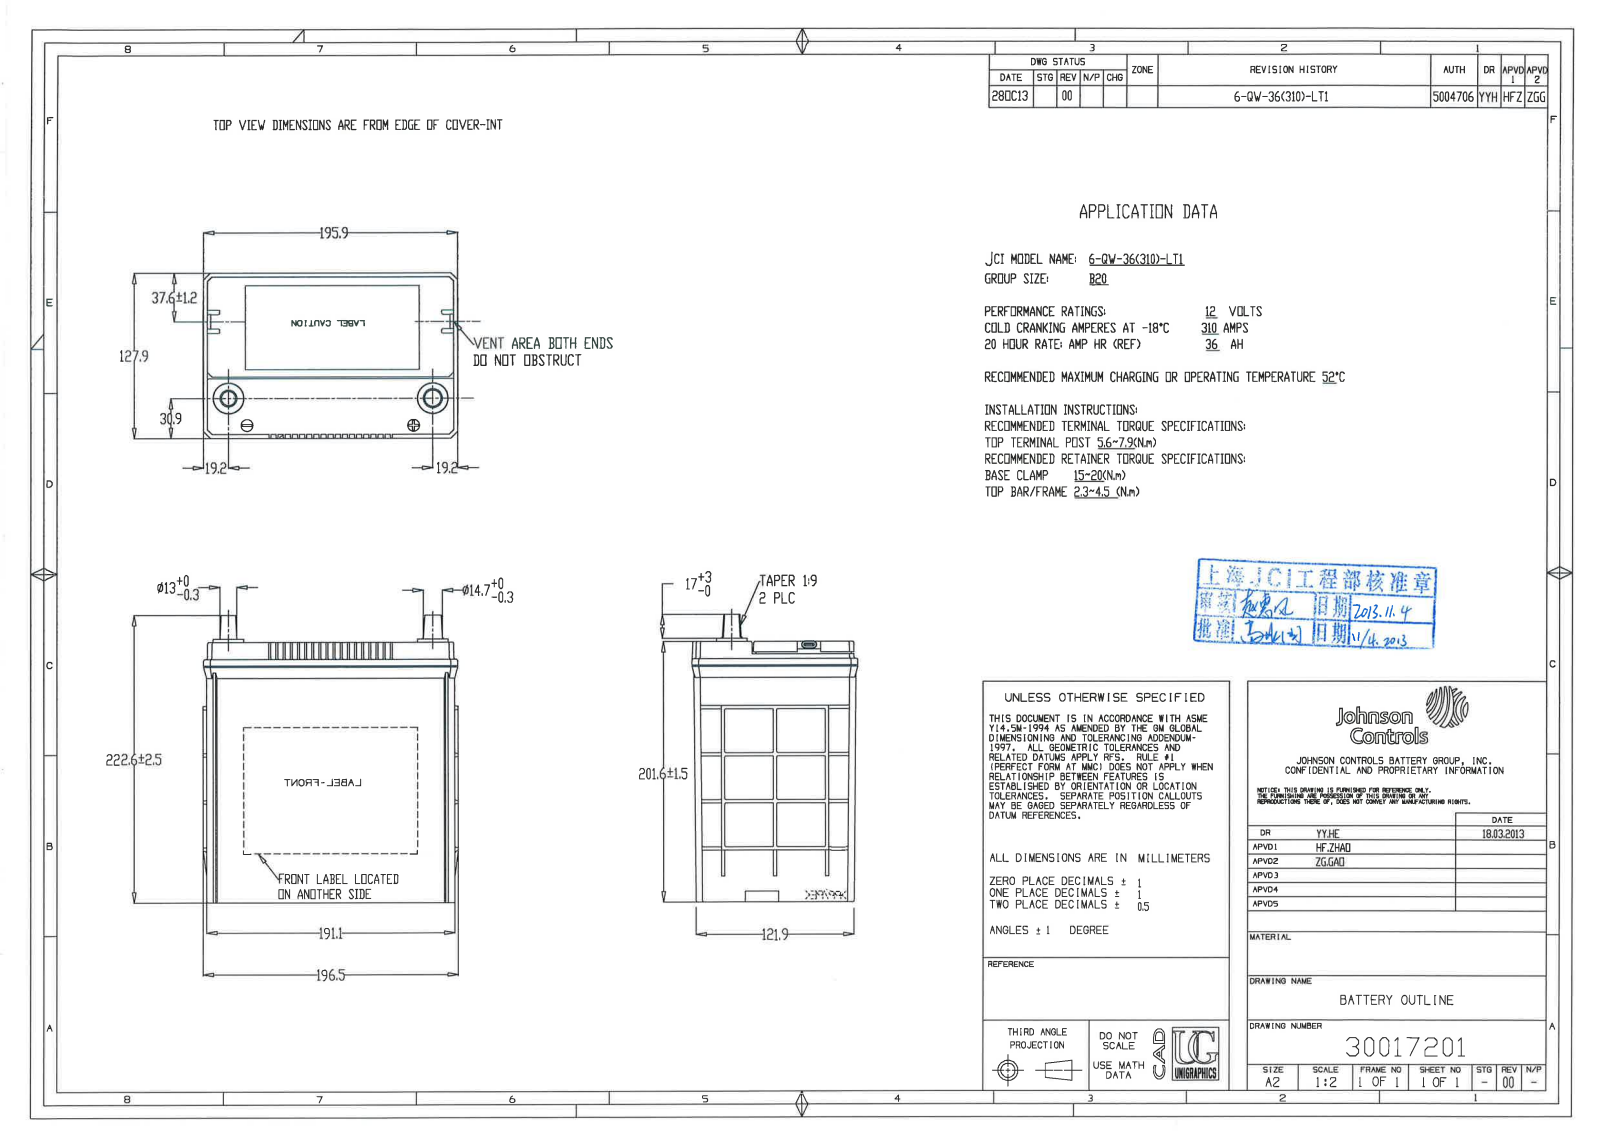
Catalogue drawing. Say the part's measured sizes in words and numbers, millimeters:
The part is named "bxus2B0Eaa1o". Its 3-D file was written by "EDS PLM SOLUTIONS - UNIGRAPHICS NX 2.0 (AUTOMOTIVE_DESIGN)". It is 10 solids with 7201 faces: 1965 planar, 2907 cylindrical and 2329 other. Overall it measures 223 by 186.7 by 126.5 millimeters. Its volume is 718 355 cubic millimeters and its surface area 657 078 square millimeters. Round holes: 6 of diameter 19.05, 2 of diameter 16, 2 of diameter 19.5, 1 of diameter 5.8, 1 of diameter 10.45, 1 of diameter 20.4. Round bosses or shafts: 56 of diameter 0.91, 1 of diameter 24, 1 of diameter 10.3. Partial cylindrical surfaces (rounded edges, fillets, slot ends): 762 of radius 0.5, 243 of radius 0.3, 222 of radius 0.51, 118 of radius 1, 116 of radius 0.76, 105 of radius 0.2, 40 of radius 1.02, 28 of radius 3. The main face-to-face distances are 29.8, 59.6, 89.4, 119.2, 119.5, 202, 179.9, 2.04, 199.96, 187.41. The hole center spacings are 29.8, 59.6, 89.4, 33.16, 44.22, 53.9, 67.72, 94.84.
